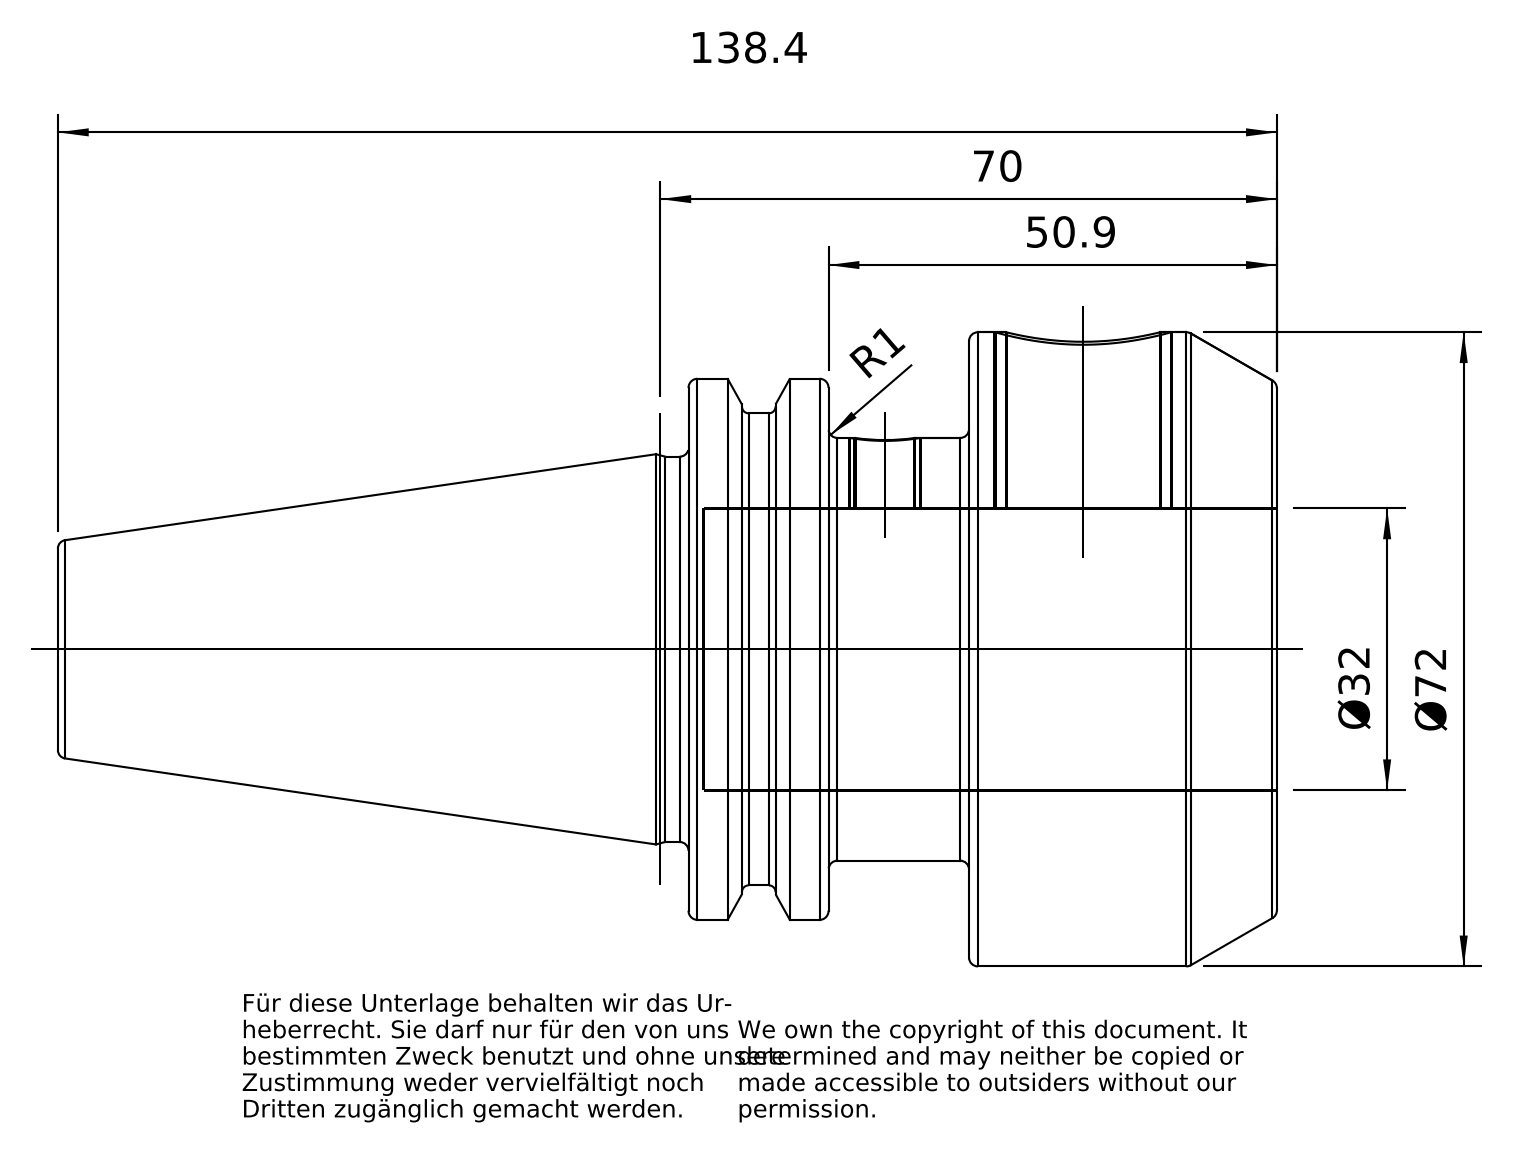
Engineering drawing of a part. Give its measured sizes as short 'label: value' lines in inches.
name: 40-305-32
written by: PRO/ENGINEER BY PARAMETRIC TECHNOLOGY CORPORATION, 2010430 (CONFIG_CONTROL_DESIGN)
unit: in
bodies: 1 solid, 111 faces (24 planar, 34 cylindrical, 53 other)
size: 5.443 × 2.835 × 2.835
volume: 13.01 in³; area: 65.64 in²
holes: 2× ⌀0.689, 1× ⌀0.268, 1× ⌀0.315, 1× ⌀0.545, 1× ⌀0.67, 1× ⌀0.787, 1× ⌀1.26
bosses: 1× ⌀2.835, 1× ⌀1.89, 1× ⌀1.722, 1× ⌀0.63
rounds: 1× R0.053, 1× R1.102, 1× R1.25
face distances: 1.376, 1.254, 2.63, 0.624, 0.63, 2.006, 0.067, 0.557, 1.187, 2.563
hole spacings: 0.886
